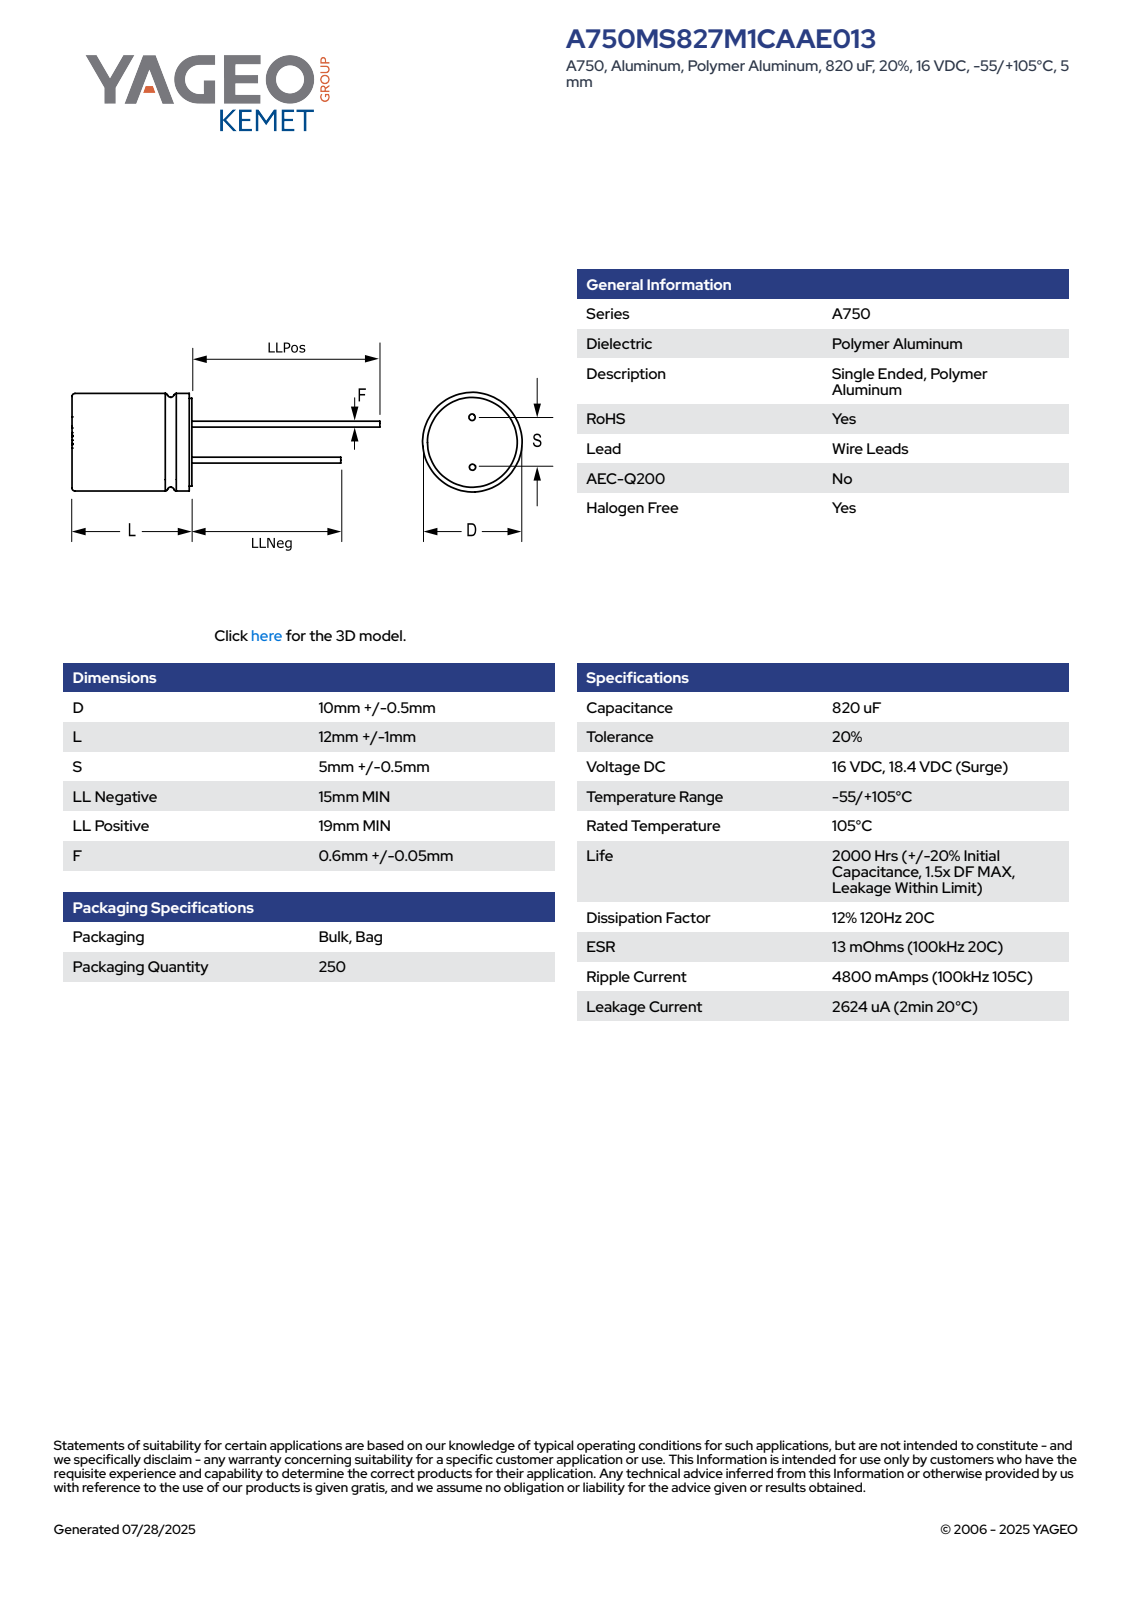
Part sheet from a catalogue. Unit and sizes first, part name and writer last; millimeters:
Units: millimetres
Overall size (bounding box): 32.01 × 10.5 × 10.5
Round bosses / shafts (diameter × count): ⌀0.65 ×2, ⌀10.5 ×1
Main face-to-face distances: 13, 13.01, 28.01, 32.01, 28, 32, 15, 19, 4, 1.15
Volume: 1 128 mm³ · Surface area: 690 mm²
Bodies: 4 solids, 75 faces (61 planar, 8 cylindrical, 6 other)
Part name (STEP PRODUCT): CAR_KP_10X12_D10.5L13S5F0.65
STEP written by: SolidWorks 2014 (AUTOMOTIVE_DESIGN)
